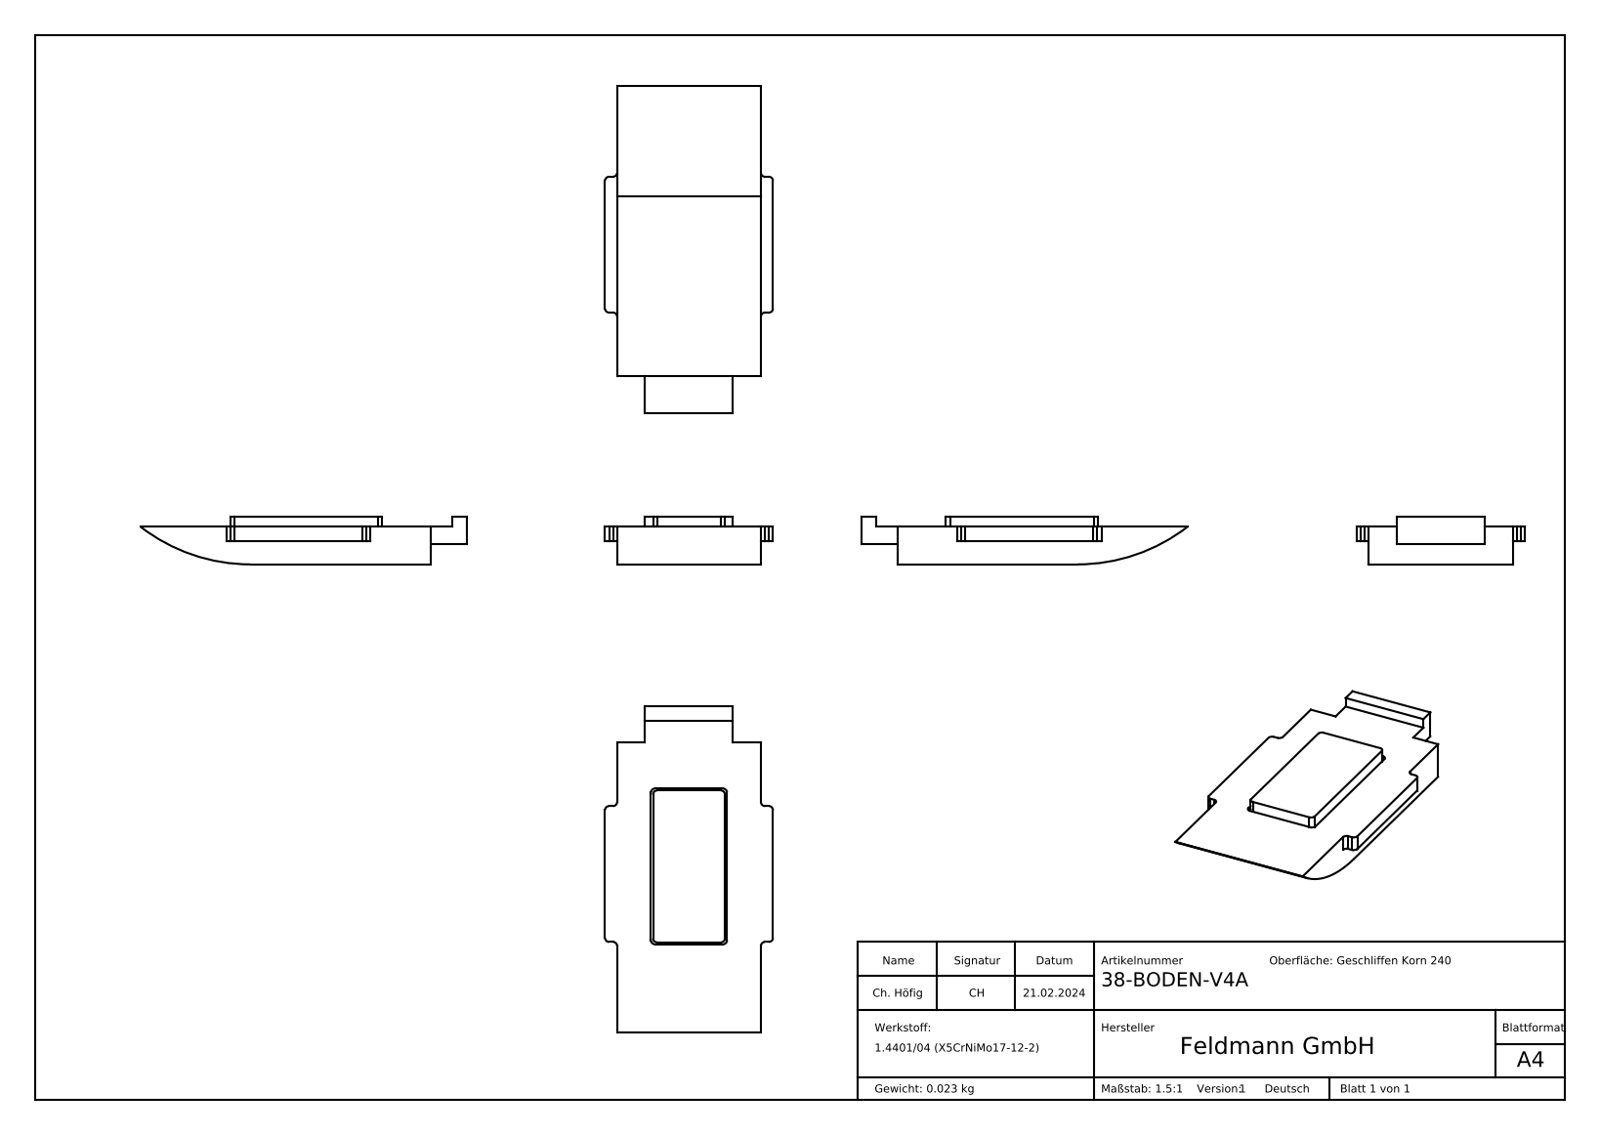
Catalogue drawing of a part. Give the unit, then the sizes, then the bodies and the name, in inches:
Units: inches
Overall size (bounding box): 1.608 × 0.827 × 0.236
Partial cylindrical surfaces — rounded edges, fillets, slot ends (radius × count): R0.02 ×16, R0.886 ×1
Main face-to-face distances: 0.187, 0.167, 0.02, 0.236, 0.069, 0.049, 0.709, 0.138, 0.073, 0.768
Volume: 0.193 in³ · Surface area: 3.799 in²
Bodies: 2 solids, 358 faces (218 planar, 17 cylindrical, 123 other)
Part name (STEP PRODUCT): 38-Boden-XXX-OG_38-BODEN-V4A Teil1; 38-Boden-GU_38-BODEN-ZN0-GU; 38-BODEN-V4A
STEP written by: SolidWorks 2018 (CONFIG_CONTROL_DESIGN)
